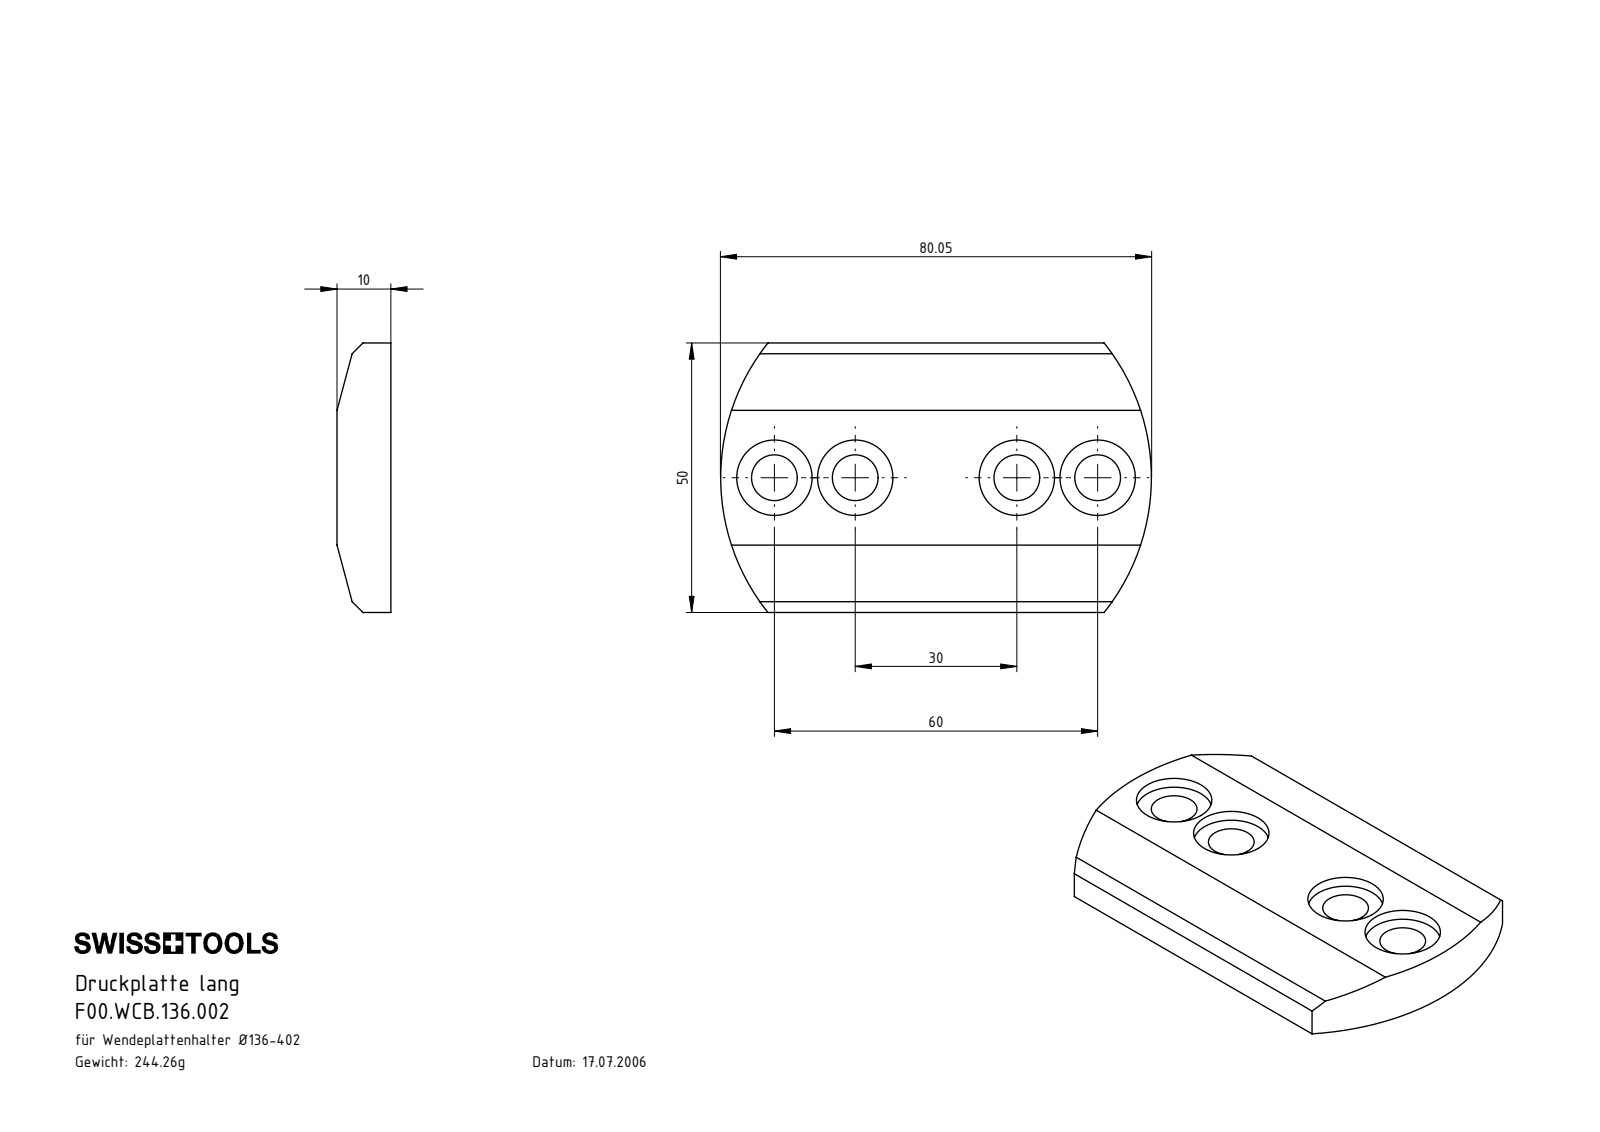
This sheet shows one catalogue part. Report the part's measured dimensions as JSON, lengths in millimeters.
{"part_name": "F00.WCB.136.002", "step_written_by": "SolidWorks 2017 (AUTOMOTIVE_DESIGN)", "units": "millimeters", "bodies": {"solids": 1, "faces": 30, "planar": 12, "cylindrical": 18, "other": 0}, "overall_size": [79.95, 50, 10], "volume_mm3": 31116, "surface_area_mm2": 9971, "round_holes": [[8.5, 4], [14, 4]], "partial_cylinders_radius": [[40, 2]], "face_to_face_distances": [10, 8, 2, 50], "hole_center_spacings": [15, 45, 30, 60]}
